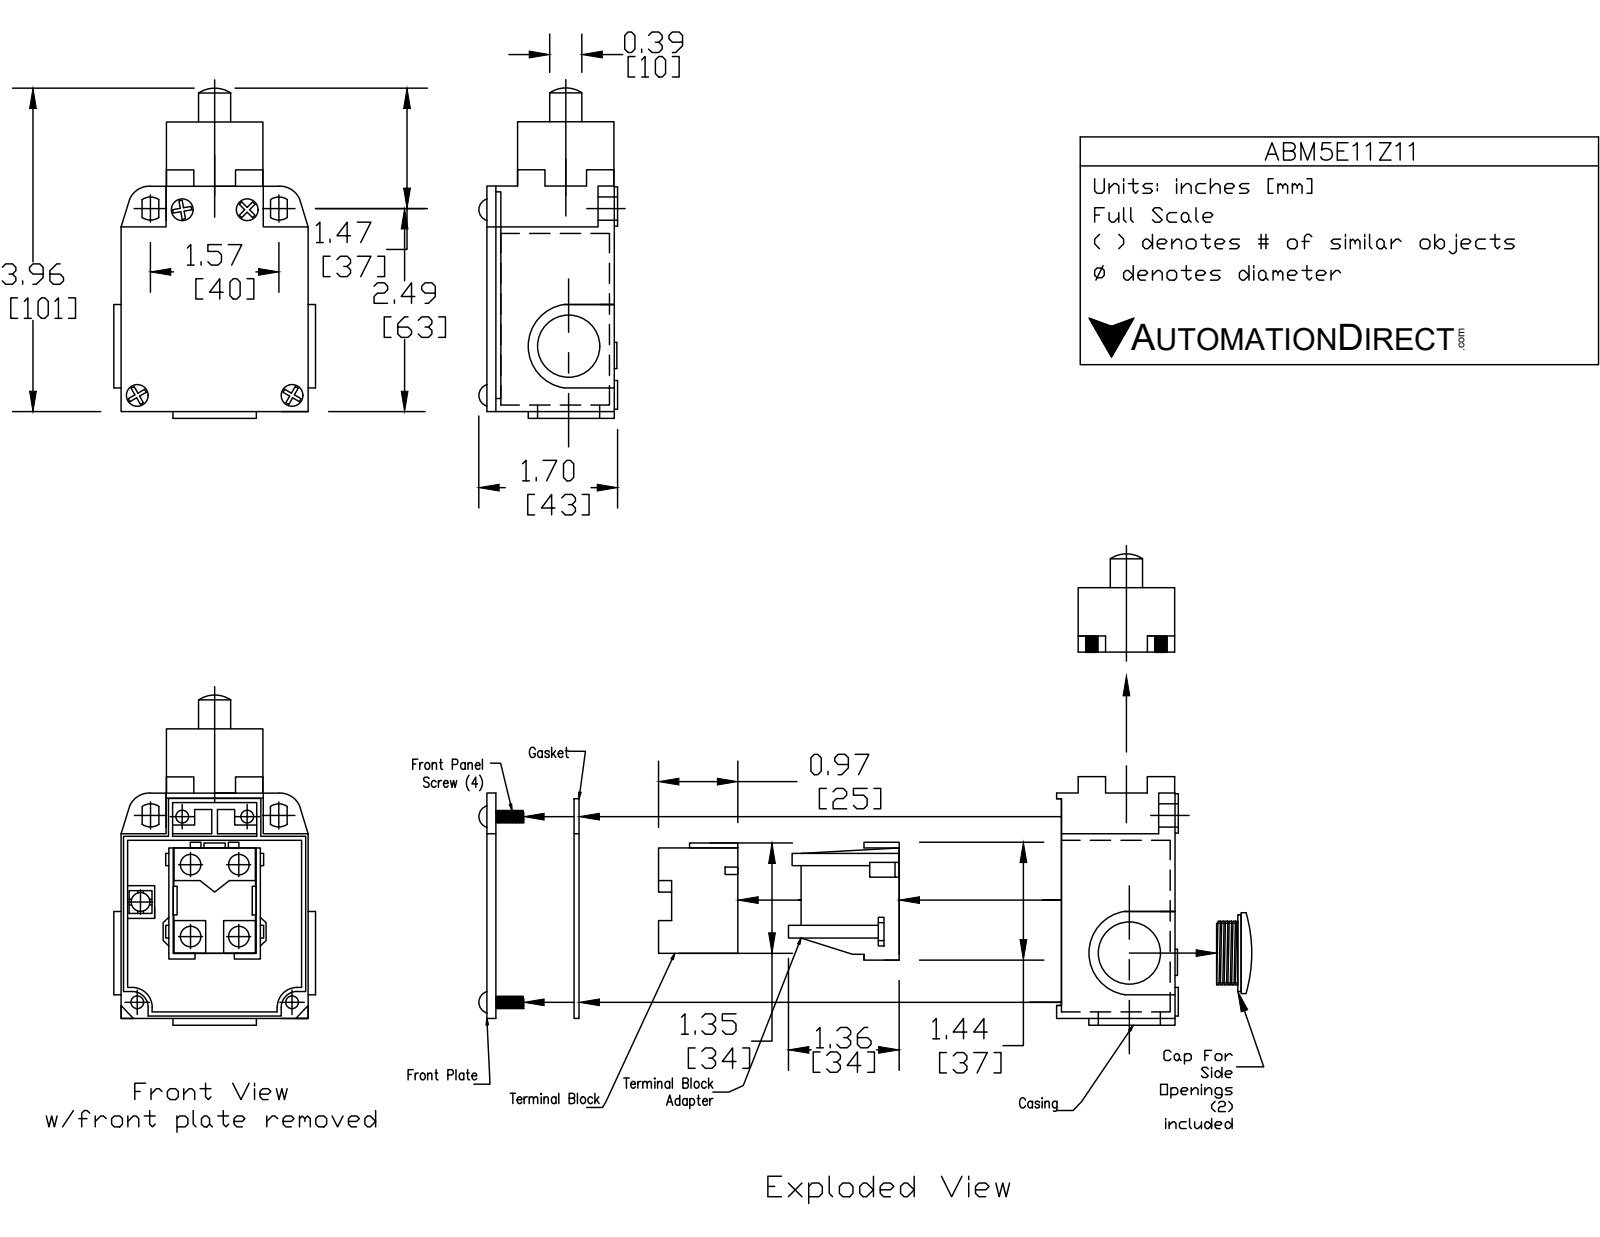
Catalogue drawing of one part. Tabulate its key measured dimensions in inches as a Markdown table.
| quantity | value |
| --- | --- |
| part name | ABM5E11Z11 |
| STEP written by | SolidWorks 2017 (AUTOMOTIVE_DESIGN) |
| units | inches |
| bodies | 3 solids, 151 faces (68 planar, 66 cylindrical, 17 other) |
| overall size | 4.196 × 1.705 × 1.575 |
| volume | 7.787 in³ |
| surface area | 37.63 in² |
| round holes (diameter × count) | 0.205 × 2, 0.394 × 1, 0.669 × 1, 0.748 × 1 |
| round bosses / shafts (diameter × count) | 0.394 × 4, 0.276 × 2 |
| partial cylindrical surfaces (radius × count) | 0.059 × 16, 0.039 × 4, 0.197 × 4, 0.128 × 2, 0.453 × 1, 0.472 × 1 |
| main face-to-face distances | 1.575, 1.555, 1.181, 0.197, 1.378, 0.374, 3.012, 3.209, 0.591, 3.031 |
| hole center spacings | 0.039, 2.641 |
